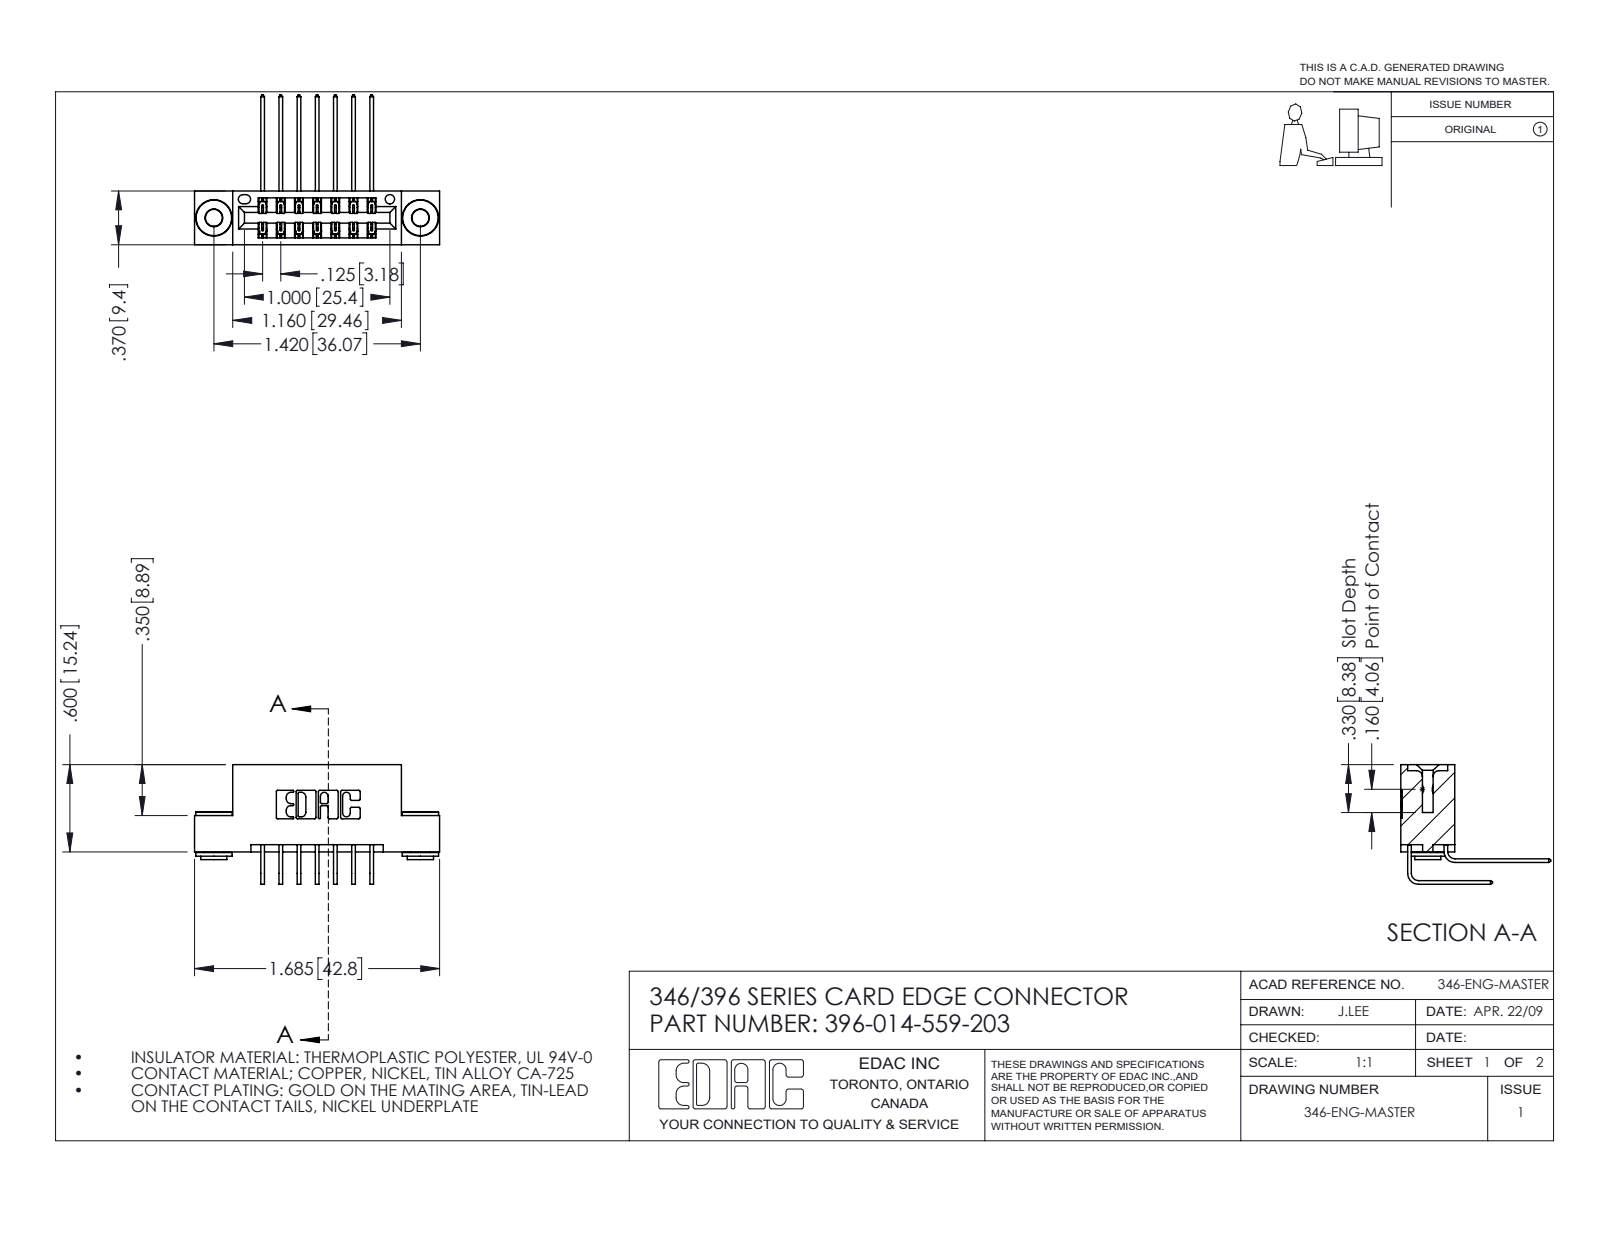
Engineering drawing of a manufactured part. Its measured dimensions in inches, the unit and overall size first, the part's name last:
Units: inches
Overall size (bounding box): 1.685 × 1.03 × 0.823
Round holes (diameter × count): ⌀0.116 ×2, ⌀0.156 ×2, ⌀0.064 ×1
Round bosses / shafts (diameter × count): ⌀0.25 ×2, ⌀0.18 ×2, ⌀0.136 ×2
Partial cylindrical surfaces — rounded edges, fillets, slot ends (radius × count): R0.01 ×22, R0.006 ×21, R0.007 ×6, R0.031 ×6, R0.026 ×3, R0.014 ×2, R0.022 ×2, R0.024 ×2
Main face-to-face distances: 0.25, 0.048, 0.322, 0.37, 0.025, 0.298, 0.072, 0.125, 0.125, 0.148
Hole centre spacings: 0.246, 1.217, 1.42
Volume: 0.244 in³ · Surface area: 8.606 in²
Bodies: 17 solids, 916 faces (604 planar, 304 cylindrical, 8 other)
Part name (STEP PRODUCT): 346 Part_Flush Mounting Lugs - 0.156 Dia-TH; 396-014-559-203; 345-250-002_345-250-002-102; 345-292-001_559 Tail - 2 (+1 more)
STEP written by: SolidWorks 2016 (CONFIG_CONTROL_DESIGN)
